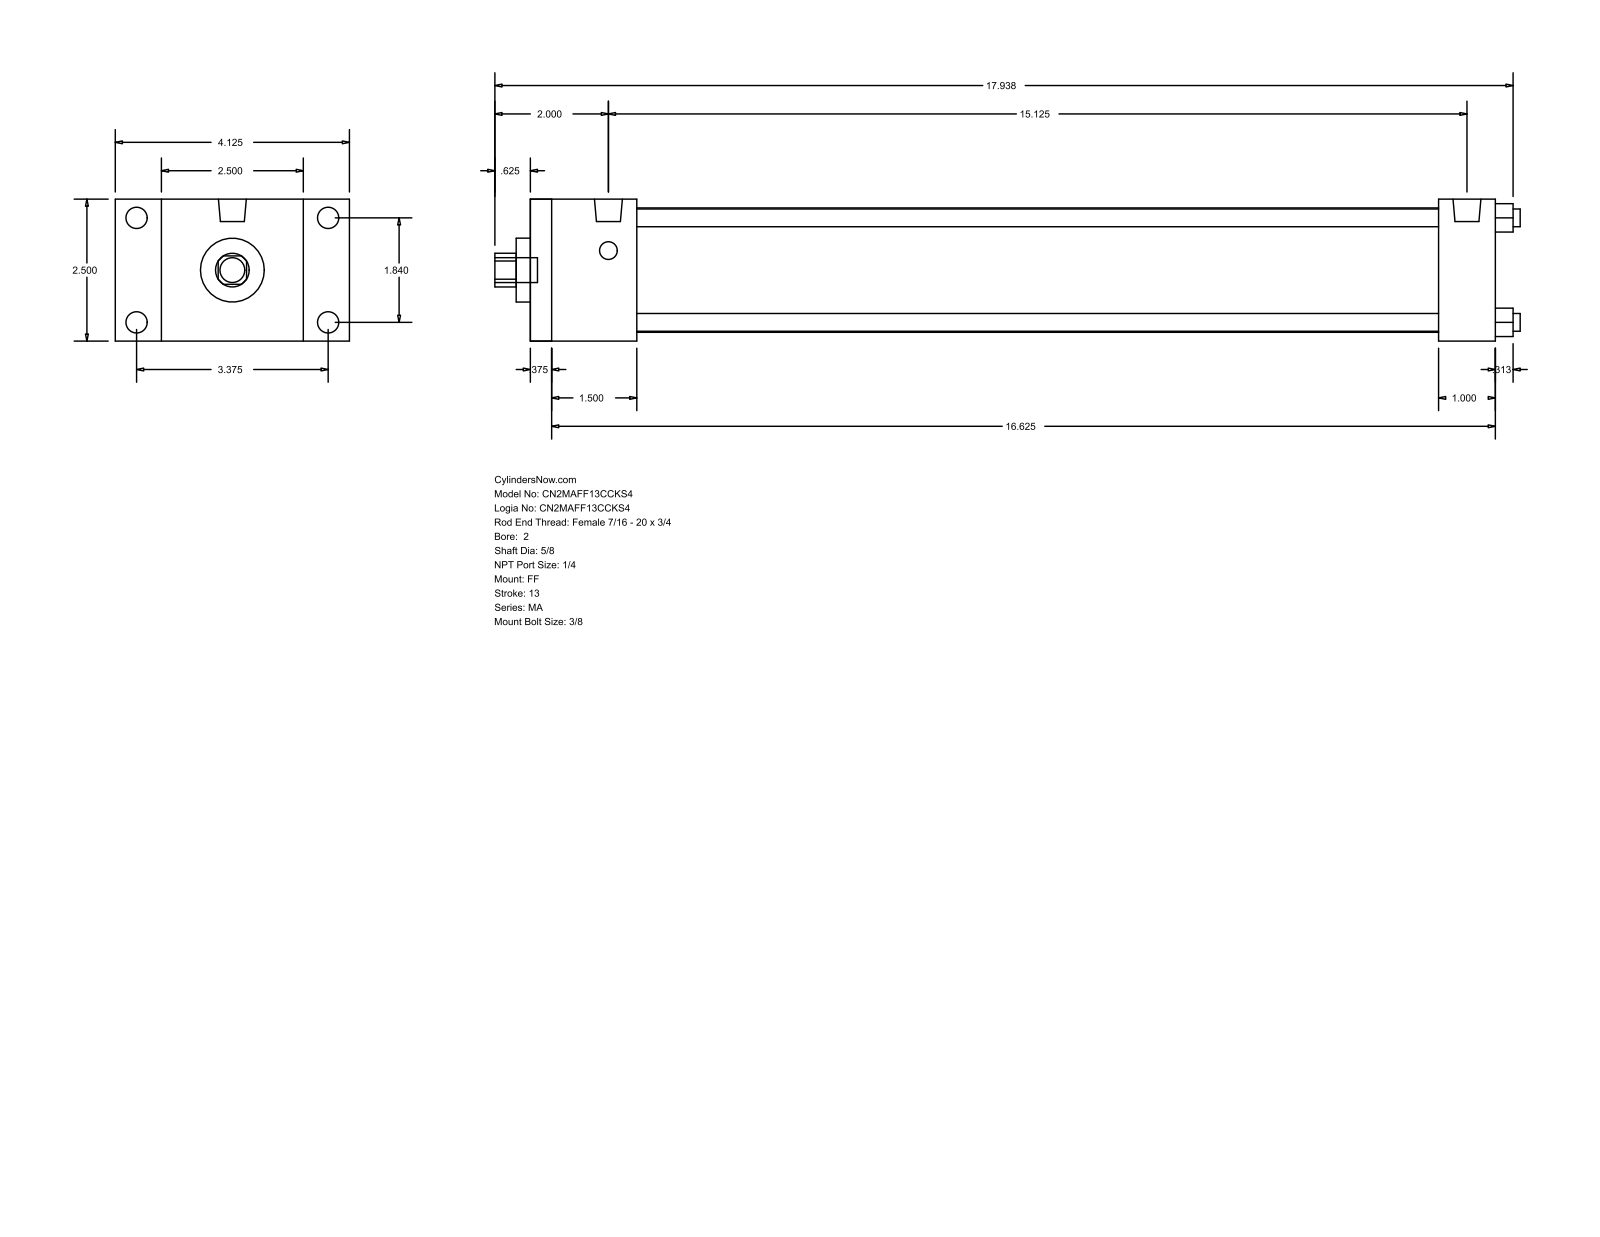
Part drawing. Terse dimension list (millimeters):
name: MA_FF__0200_0.625
written by: GSSL Pune (CONFIG_CONTROL_DESIGN)
unit: mm
bodies: 0 solids, 92 faces (64 planar, 28 cylindrical, 0 other)
size: 458.79 × 104.78 × 63.5
holes: 4× ⌀7.94, 1× ⌀15.88, 1× ⌀28.57, 1× ⌀55.63
bosses: 4× ⌀9.53, 4× ⌀7.94, 2× ⌀12.49, 1× ⌀11.11
rounds: 1× R7.54
face distances: 63.5, 431.8, 9.52, 422.28, 38.1, 47.62, 406.39, 396.87, 358.77, 384.18
hole spacings: 33.05, 46.74, 66.1
